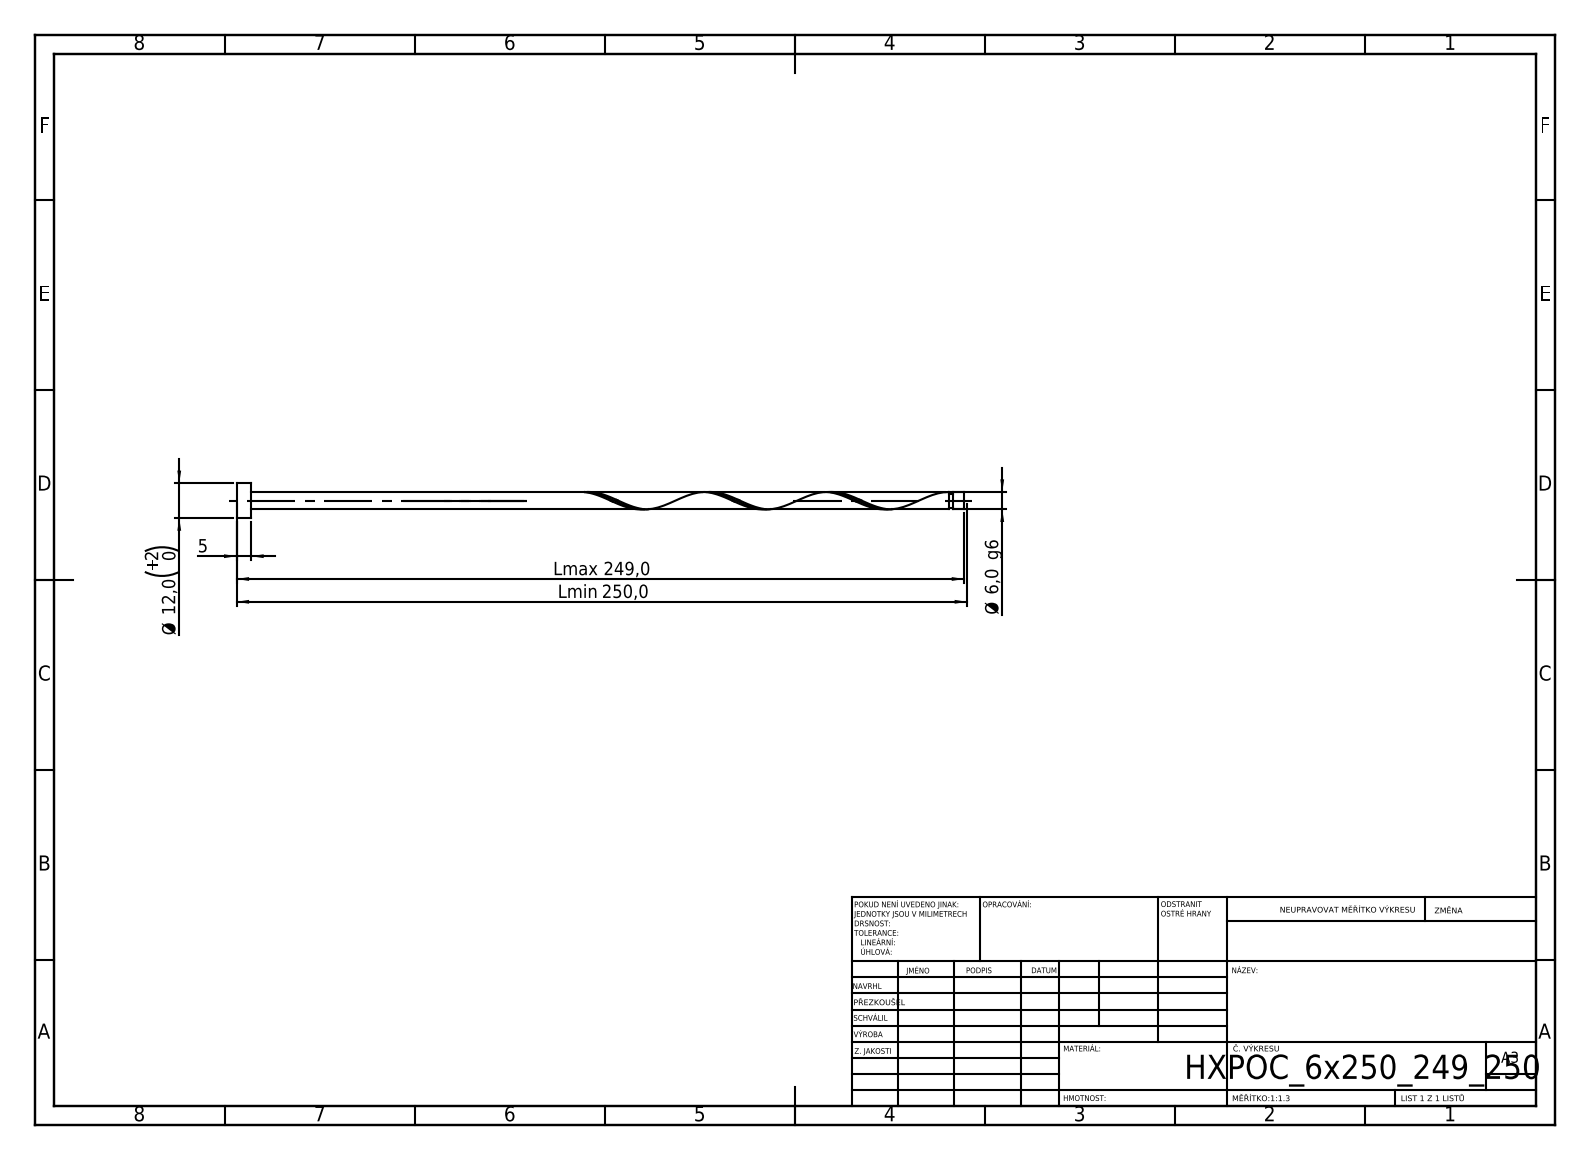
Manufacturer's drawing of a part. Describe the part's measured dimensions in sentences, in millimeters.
Its 3-D file was written by "SolidWorks 2019 (CONFIG_CONTROL_DESIGN)". It is 1 solid with 21 faces: 6 planar, 14 cylindrical and 1 other. Overall it measures 249 by 12 by 12 millimeters. Its volume is 7 385 cubic millimeters and its surface area 5 110 square millimeters. Round bosses or shafts: 1 of diameter 12, 1 of diameter 6, 1 of diameter 4.8. The main face-to-face distances are 5, 249, 244, 245.09, 240.09, 3.91, 243.89, 238.89, 1.2, 5.11.
